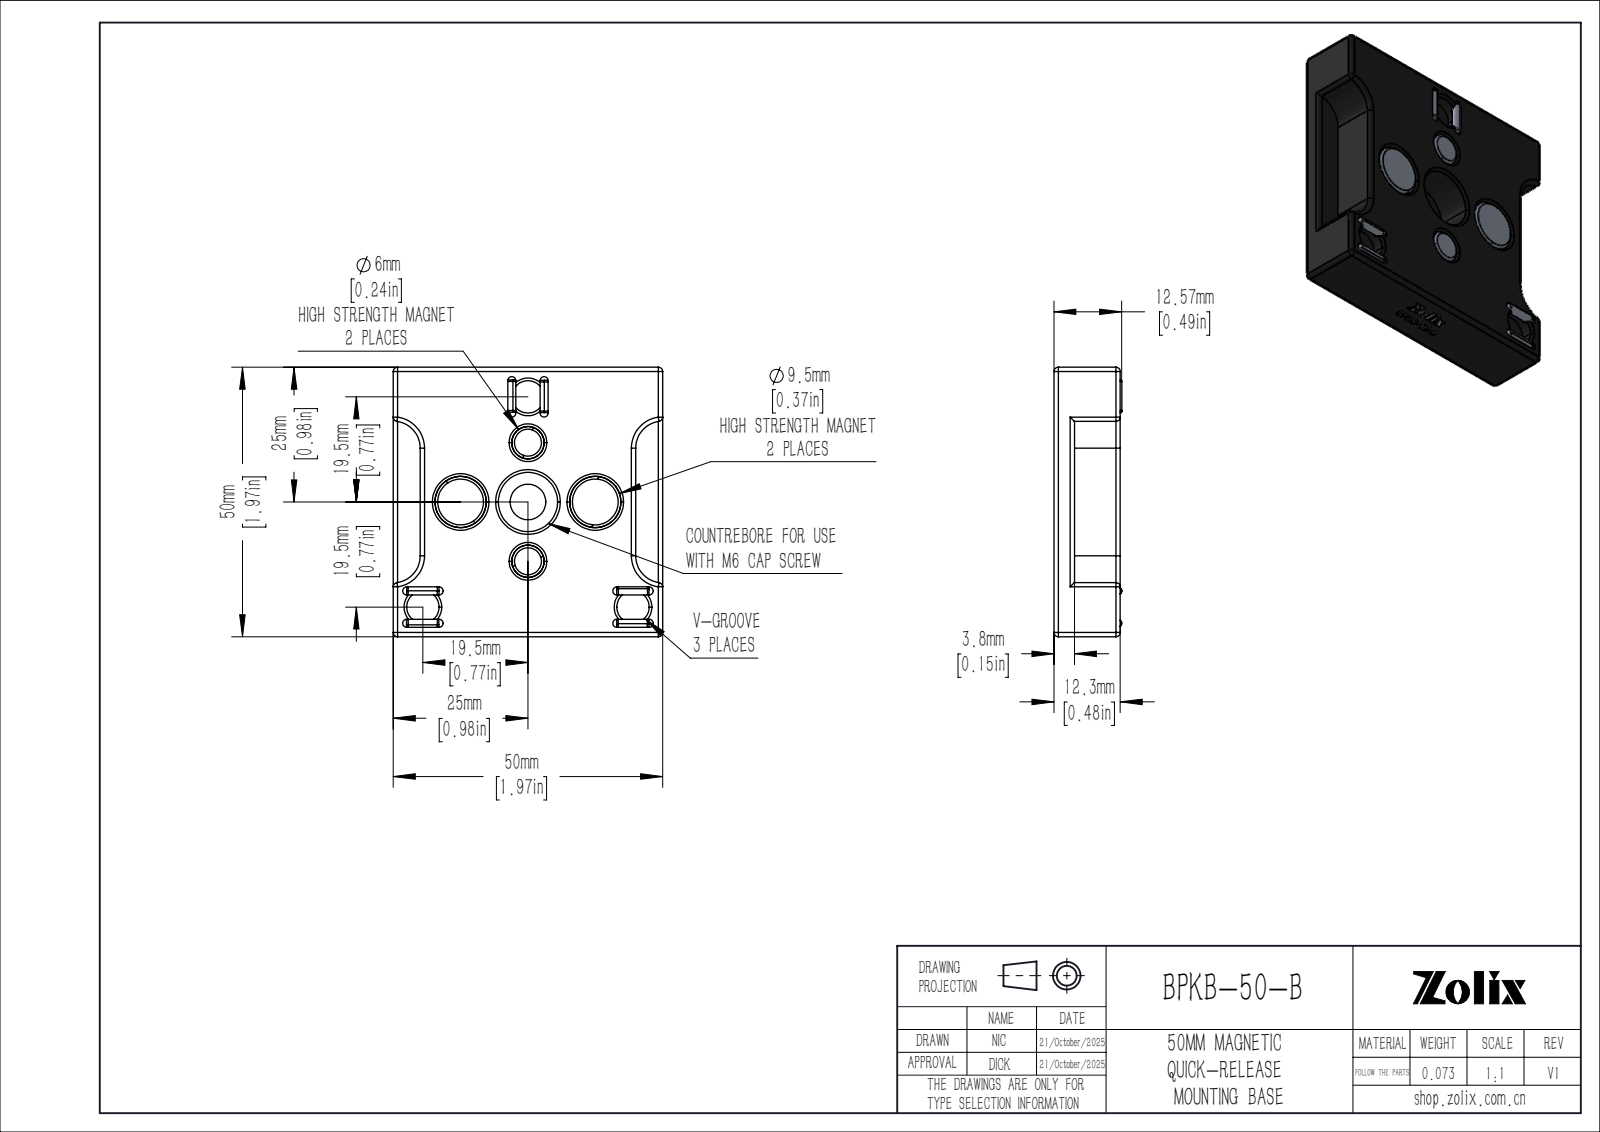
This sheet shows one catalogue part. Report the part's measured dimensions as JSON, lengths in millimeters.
{"part_name": "BPKB-50-B", "step_written_by": "SolidWorks 2020 (CONFIG_CONTROL_DESIGN)", "units": "millimeters", "bodies": {"solids": 11, "faces": 537, "planar": 295, "cylindrical": 88, "other": 154}, "overall_size": [50, 50, 12.6], "volume_mm3": 27197, "surface_area_mm2": 9343, "round_holes": [[6, 5], [2, 2], [3, 2], [9.5, 2], [6.6, 1], [11, 1]], "round_bosses_or_shafts": [[1.5, 4]], "partial_cylinders_radius": [[0.8, 20], [0.75, 12], [5, 4]], "face_to_face_distances": [12.3, 50, 45, 5, 3.8, 5.95, 6.35, 2.15, 8.5, 40], "hole_center_spacings": [16.65, 11, 12.5, 20.72, 21.27, 23.16, 27.58, 36.2]}
